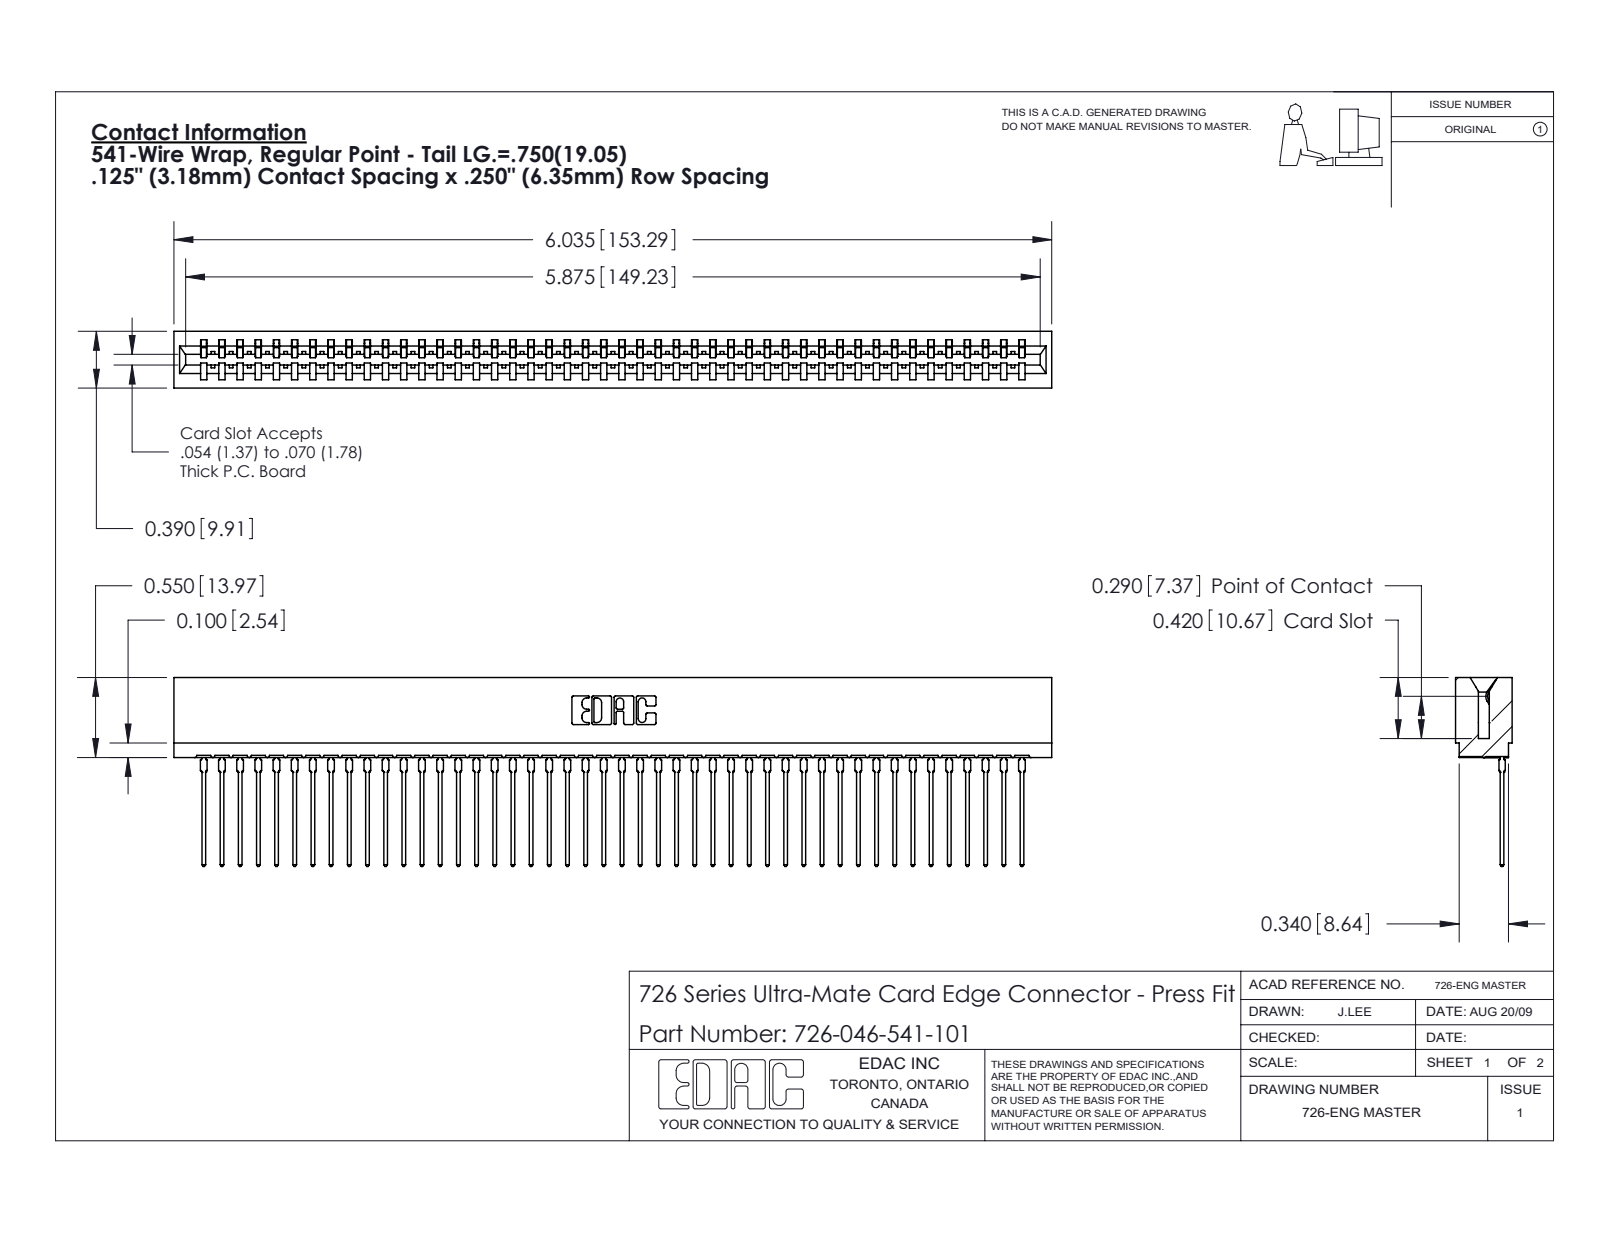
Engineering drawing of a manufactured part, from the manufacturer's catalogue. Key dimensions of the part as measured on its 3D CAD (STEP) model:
Part name (STEP PRODUCT): 726-046-541-101; 726 Part_.515 Slot Depth - 01; 746-292-001_541
STEP written by: SolidWorks 2020 (CONFIG_CONTROL_DESIGN)
Units: inches
Bodies: 47 solids, 5065 faces (2953 planar, 916 cylindrical, 1196 other)
Overall size (bounding box): 6.035 × 1.299 × 0.39
Volume: 0.847 in³ · Surface area: 34.64 in²
Partial cylindrical surfaces — rounded edges, fillets, slot ends (radius × count): R0.021 ×92, R0.015 ×47, R0.01 ×22, R0.007 ×6, R0.031 ×6, R0.005 ×4, R0.011 ×4, R0.026 ×3
Main face-to-face distances: 0.057, 0.333, 0.39, 0.025, 0.307, 0.25, 0.083, 0.275, 0.365, 0.032
